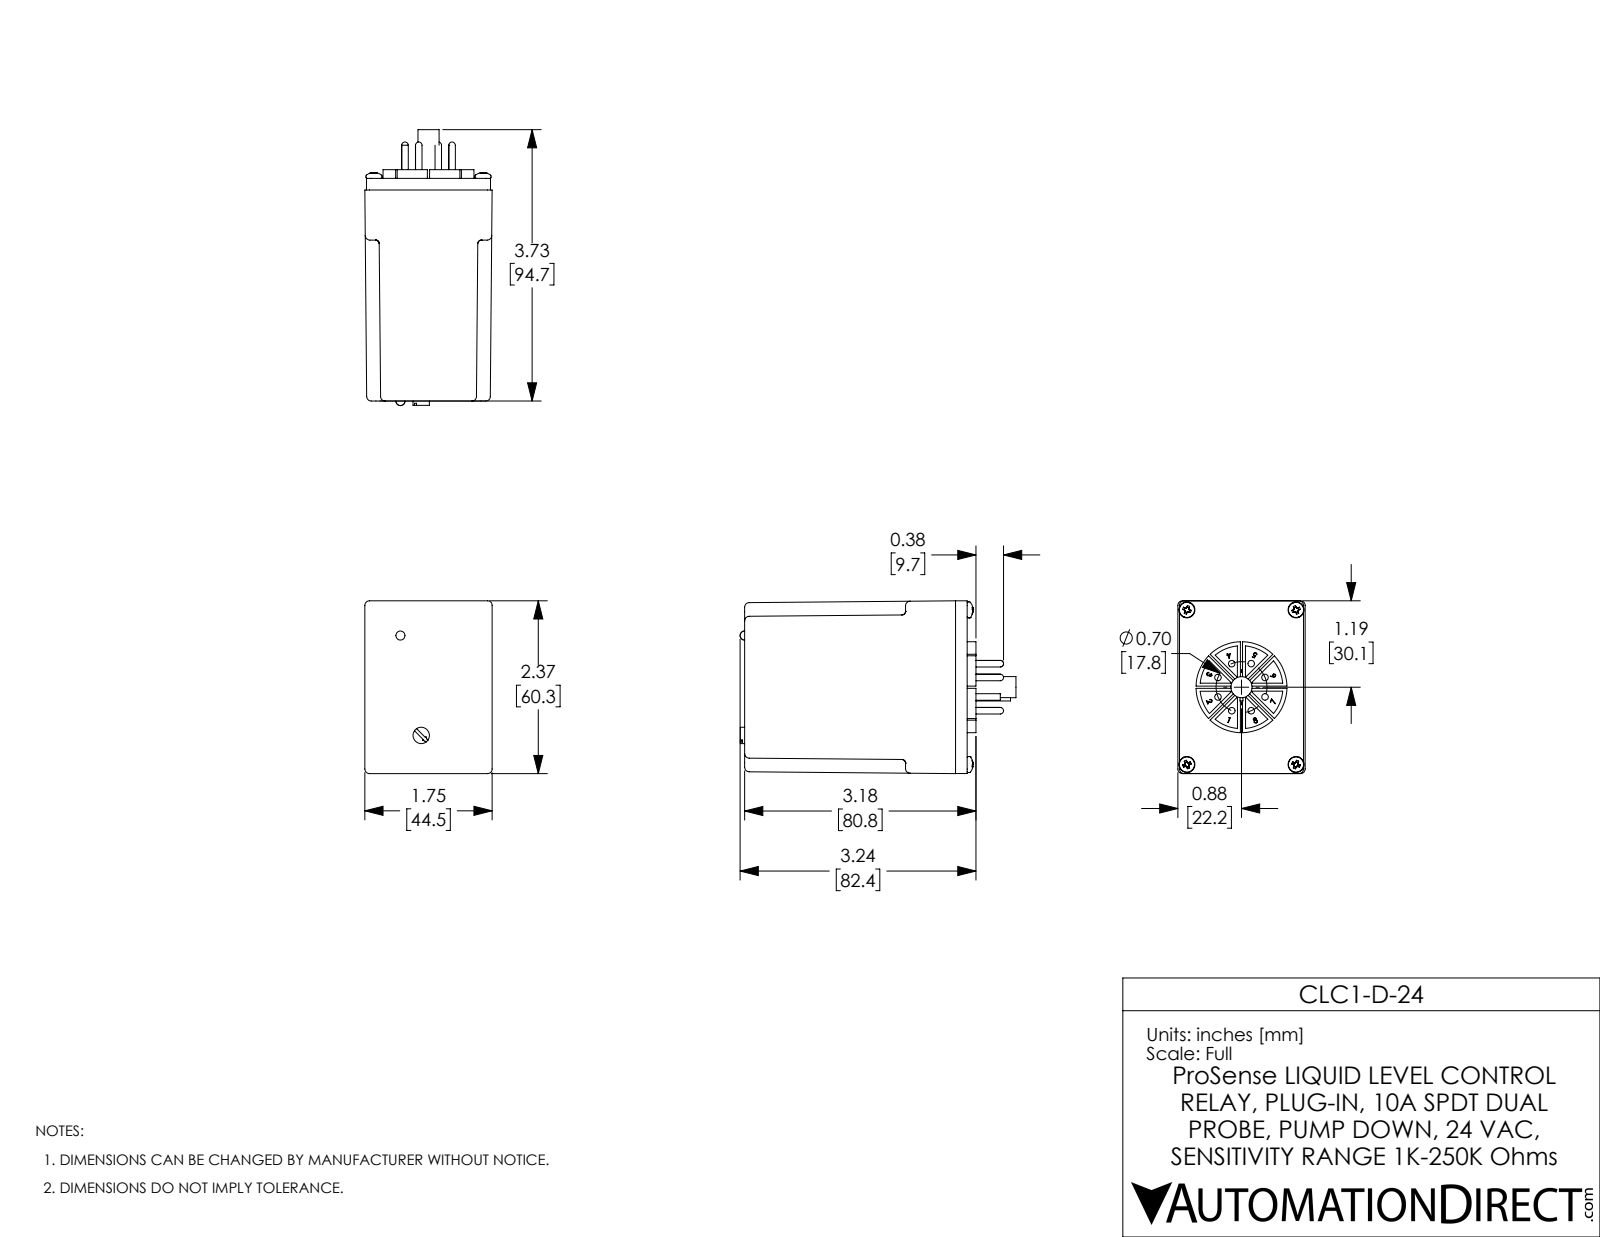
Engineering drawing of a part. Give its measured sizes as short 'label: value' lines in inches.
name: CLC1-D-24
written by: SolidWorks 2017 (AUTOMOTIVE_DESIGN)
unit: in
bodies: 16 solids, 706 faces (229 planar, 294 cylindrical, 183 other)
size: 3.79 × 2.375 × 1.75
volume: 12.24 in³; area: 44.72 in²
holes: 4× ⌀0.125
bosses: 8× ⌀0.09, 4× ⌀0.219, 4× ⌀0.112, 4× ⌀0.08, 1× ⌀1.25, 1× ⌀0.29, 1× ⌀0.225
rounds: 32× R0.063, 8× R0.005, 4× R0.05, 1× R0.57
face distances: 2.9, 0.16, 3.06, 0.07, 0.23, 3.13, 0.188, 0.03, 3.18, 0.05
hole spacings: 1.5, 2.125, 2.601
